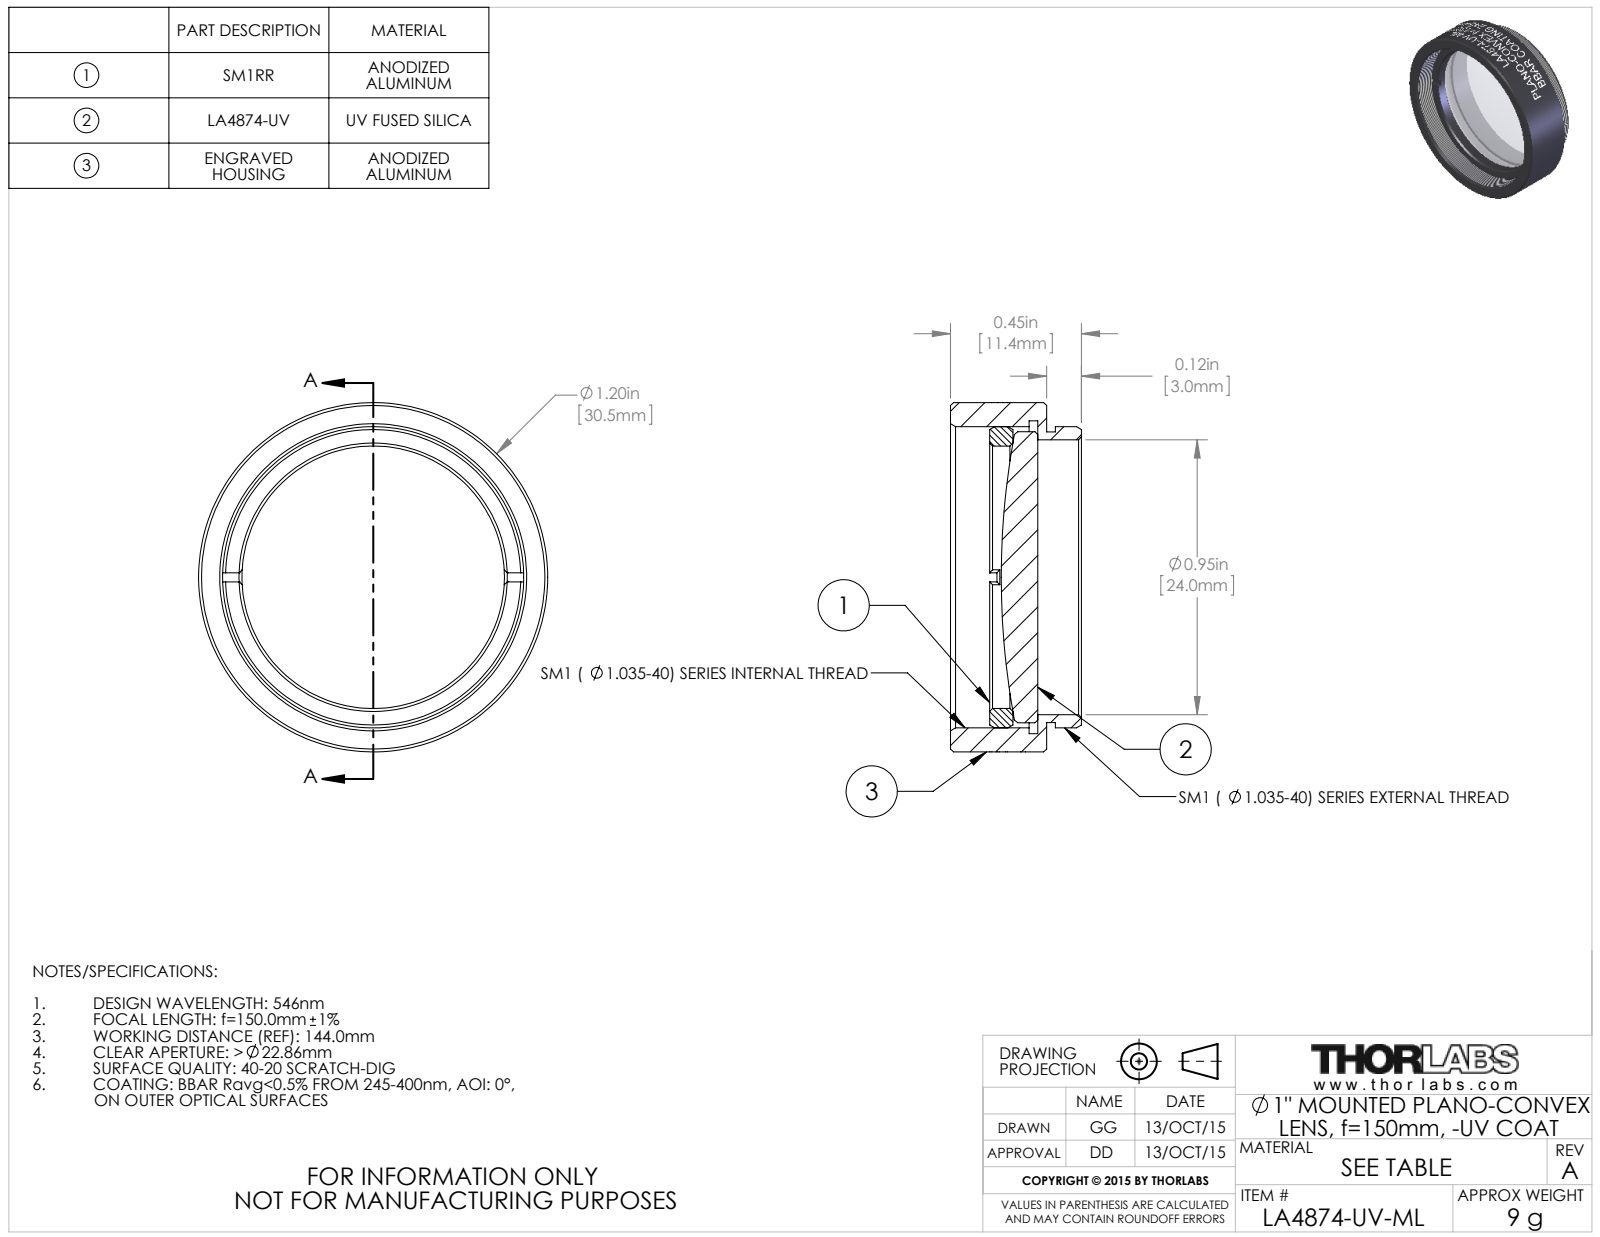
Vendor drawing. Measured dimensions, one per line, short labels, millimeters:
name: TTN039422-E0W
written by: SolidWorks 2014 (CONFIG_CONTROL_DESIGN)
unit: mm
bodies: 3 solids, 162 faces (20 planar, 114 cylindrical, 28 other)
size: 30.48 × 30.48 × 11.43
volume: 3 393 mm³; area: 4 296 mm²
holes: 1× ⌀22.91, 1× ⌀24, 1× ⌀27.31
bosses: 1× ⌀30.48, 1× ⌀26.29, 1× ⌀25.4, 1× ⌀25.37
face distances: 0.76, 8.38, 7.62, 2.94, 2.18, 5.44, 4.98, 4.22, 2.04, 3.4
